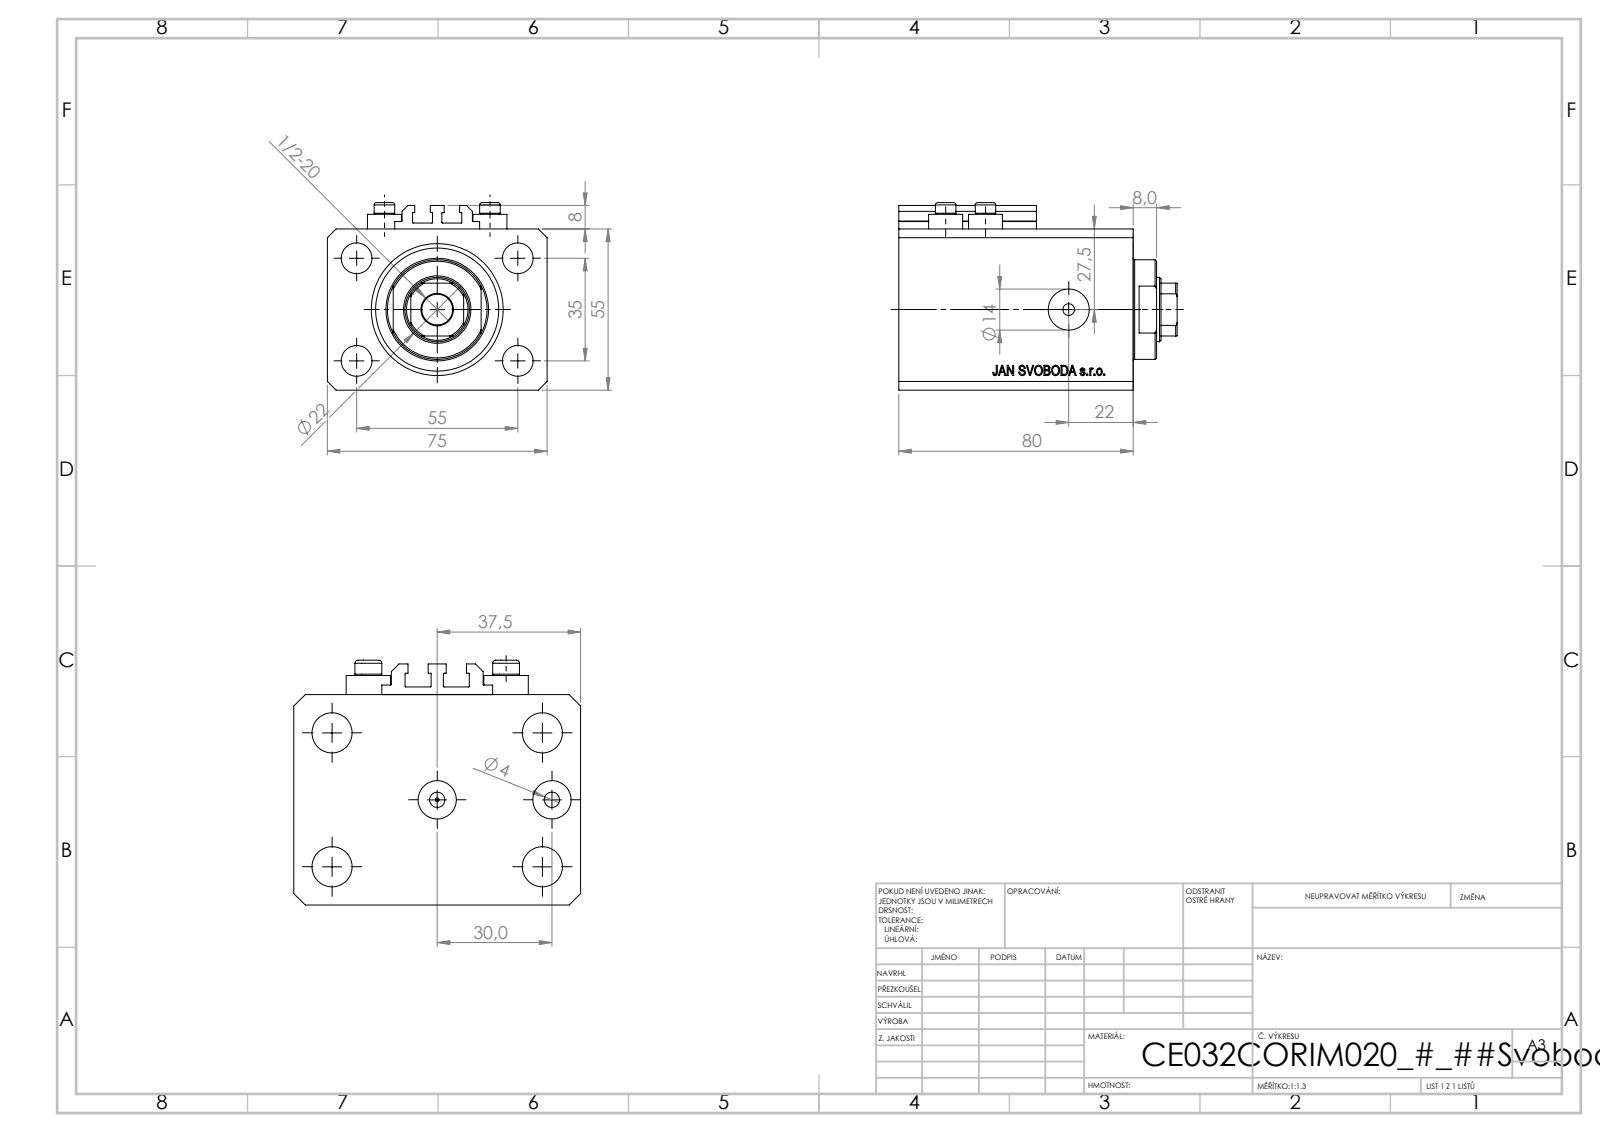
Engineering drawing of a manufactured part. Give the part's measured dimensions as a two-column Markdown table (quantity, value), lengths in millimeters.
| quantity | value |
| --- | --- |
| part name | ALLEN BOLT V250CE; V250CE_VC_C; V250CE_C_VCP; V250CE_C_Body |
| STEP written by | SolidWorks 2019 (CONFIG_CONTROL_DESIGN) |
| units | millimeters |
| bodies | 8 solids, 1042 faces (504 planar, 92 cylindrical, 446 other) |
| overall size | 95 × 75 × 64 |
| volume | 304 608 mm³ |
| surface area | 71 883 mm² |
| round holes (diameter × count) | 4 × 8, 10.5 × 5, 10 × 2, 14 × 2, 1.25 × 1, 22 × 1, 32 × 1, 45 × 1 |
| round bosses / shafts (diameter × count) | 11.6 × 4, 7 × 4, 34 × 1 |
| partial cylindrical surfaces (radius × count) | 0.2 × 10, 10.5 × 1 |
| main face-to-face distances | 55, 75, 80, 15, 65, 9.9, 55.1, 70.1, 3, 8 |
| hole center spacings | 32.6, 36, 13.6, 17.68, 35, 38.48, 55, 60.1 |
